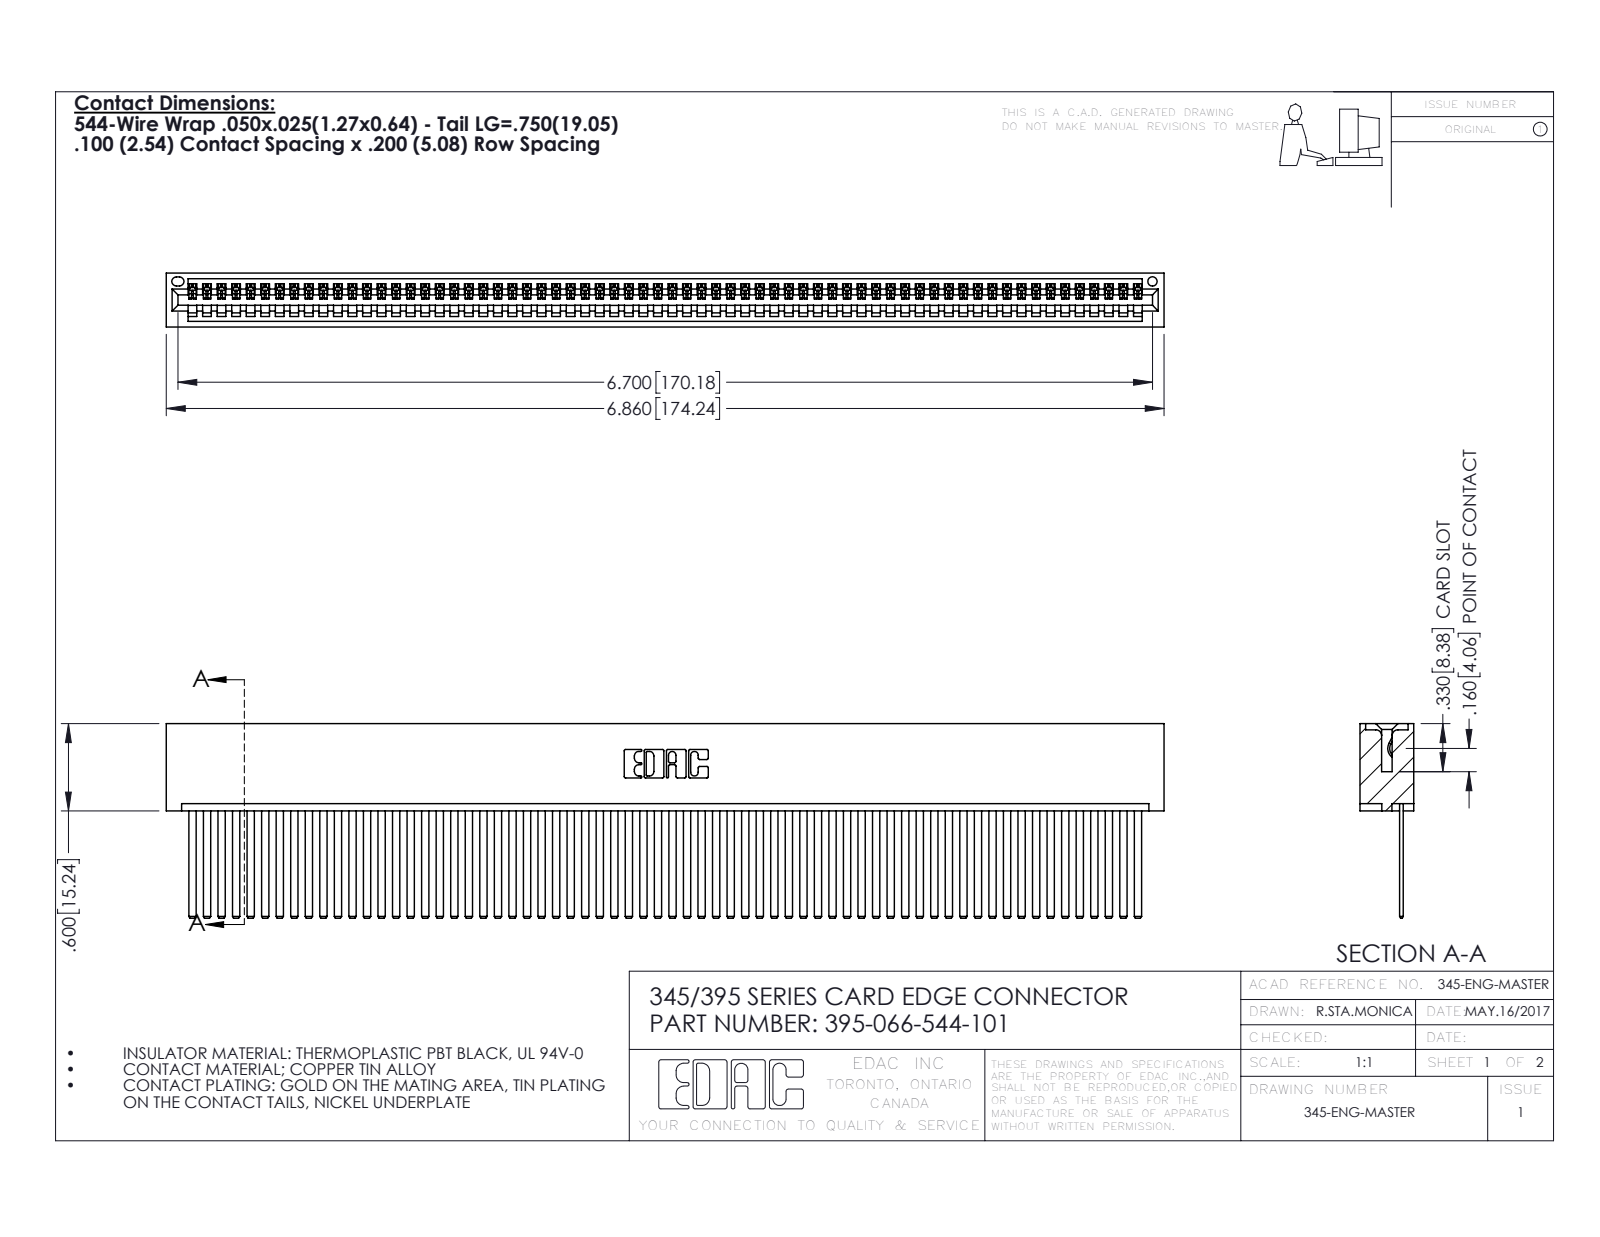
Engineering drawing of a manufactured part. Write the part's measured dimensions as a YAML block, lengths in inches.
part_name: "345 Part_No Mounting Lugs; 395-066-544-101; 345-292-001_345-293-144"
step_written_by: "SolidWorks 2016 (CONFIG_CONTROL_DESIGN)"
units: inches
bodies: {solids: 67, faces: 3550, planar: 2452, cylindrical: 1098, other: 0}
overall_size: [6.86, 1.337, 0.37]
volume: 1.104
surface_area: 41.63
round_holes:
  - {diameter: 0.064, count: 1}
partial_cylinders:
  - {radius: 0.006, count: 132}
  - {radius: 0.01, count: 22}
  - {radius: 0.007, count: 6}
  - {radius: 0.031, count: 6}
  - {radius: 0.026, count: 3}
  - {radius: 0.031, count: 2}
  - {radius: 0.04, count: 2}
  - {radius: 0.014, count: 1}
face_to_face_distances: [0.072, 0.298, 0.025, 0.098, 0.272, 0.37, 0.2, 0.225, 0.149, 0.072]
